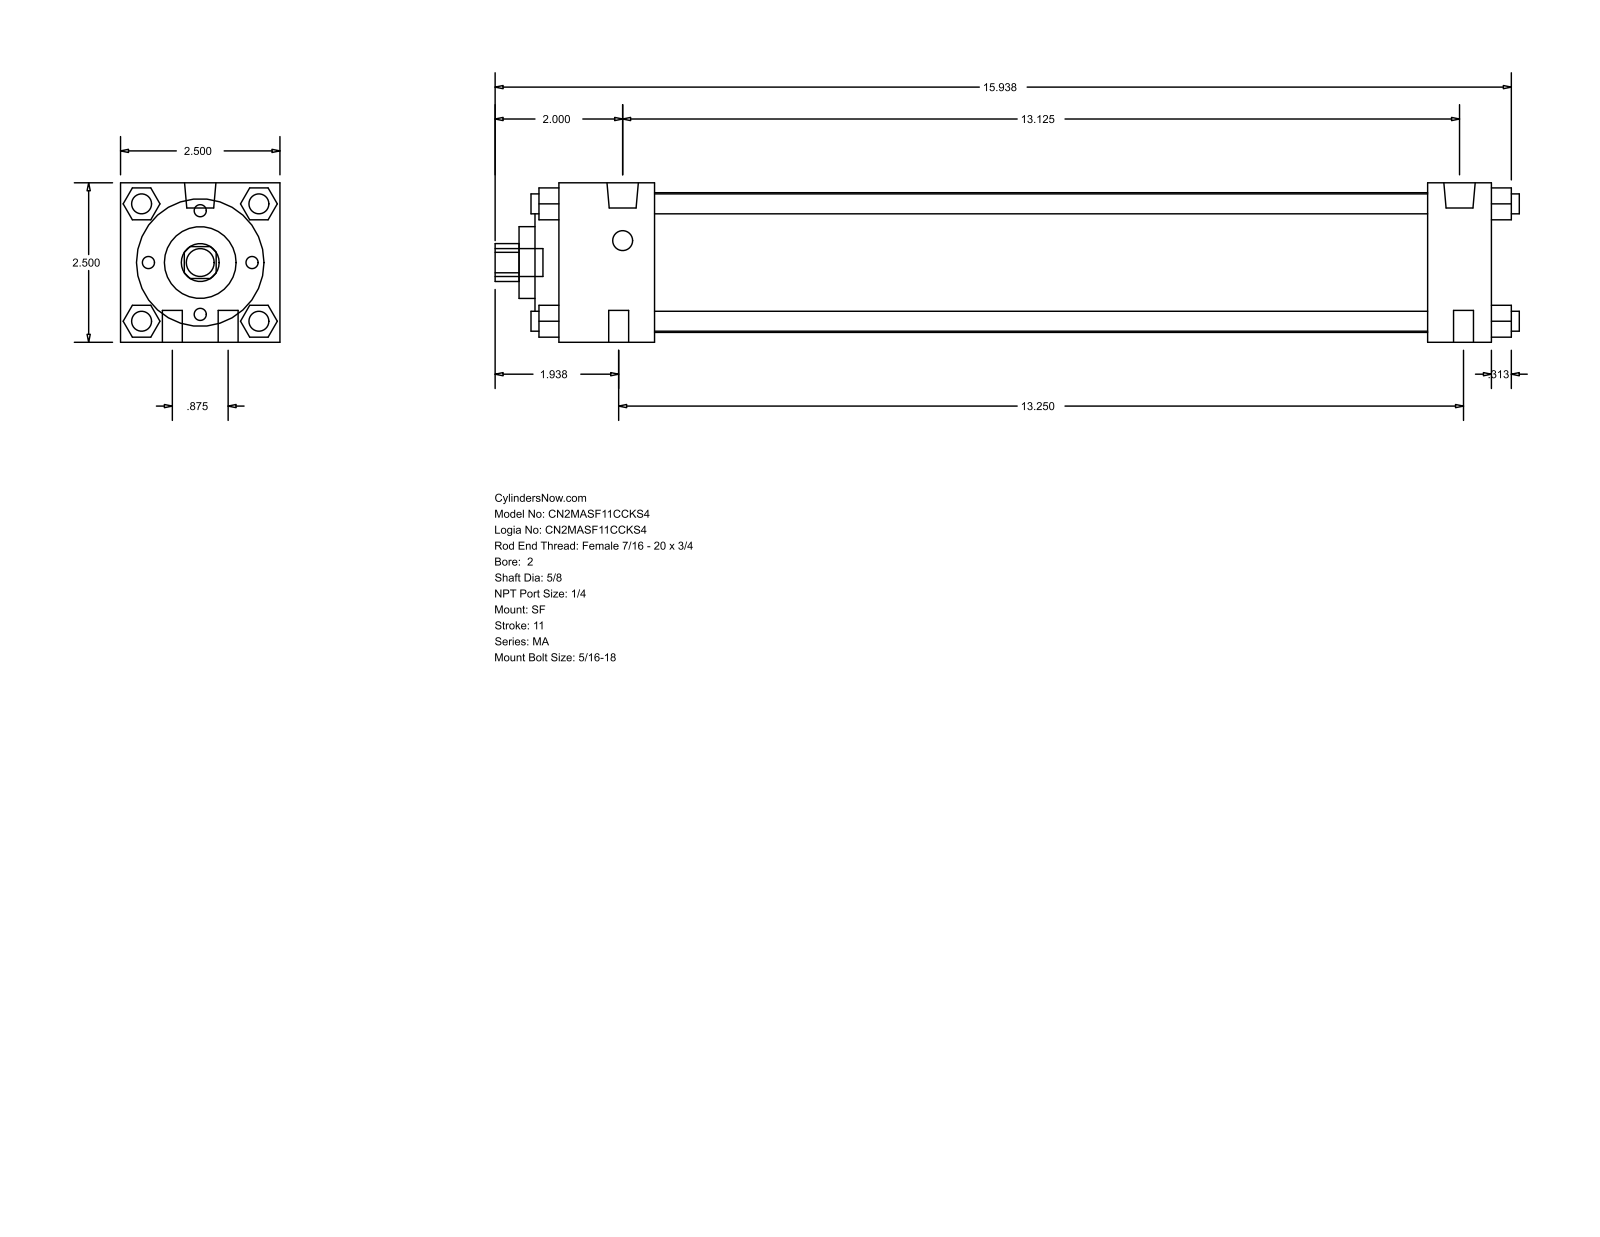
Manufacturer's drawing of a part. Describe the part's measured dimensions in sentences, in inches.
The part is named "MA_SF__0200_0.625". Its 3-D file was written by "GSSL Pune (CONFIG_CONTROL_DESIGN)". It is 0 solids with 126 faces: 95 planar, 31 cylindrical and 0 other. Overall it measures 16.063 by 2.5 by 2.5 inches. Round holes: 1 of diameter 0.625, 1 of diameter 1.125, 1 of diameter 2, 1 of diameter 2.19. Round bosses or shafts: 10 of diameter 0.313, 2 of diameter 0.492, 1 of diameter 0.437. Partial cylindrical surfaces (rounded edges, fillets, slot ends): 1 of radius 0.297. The main face-to-face distances are 2.5, 0.5, 1, 1.5, 14.625, 0.375, 13.625, 12.125, 13.125, 1.875.
